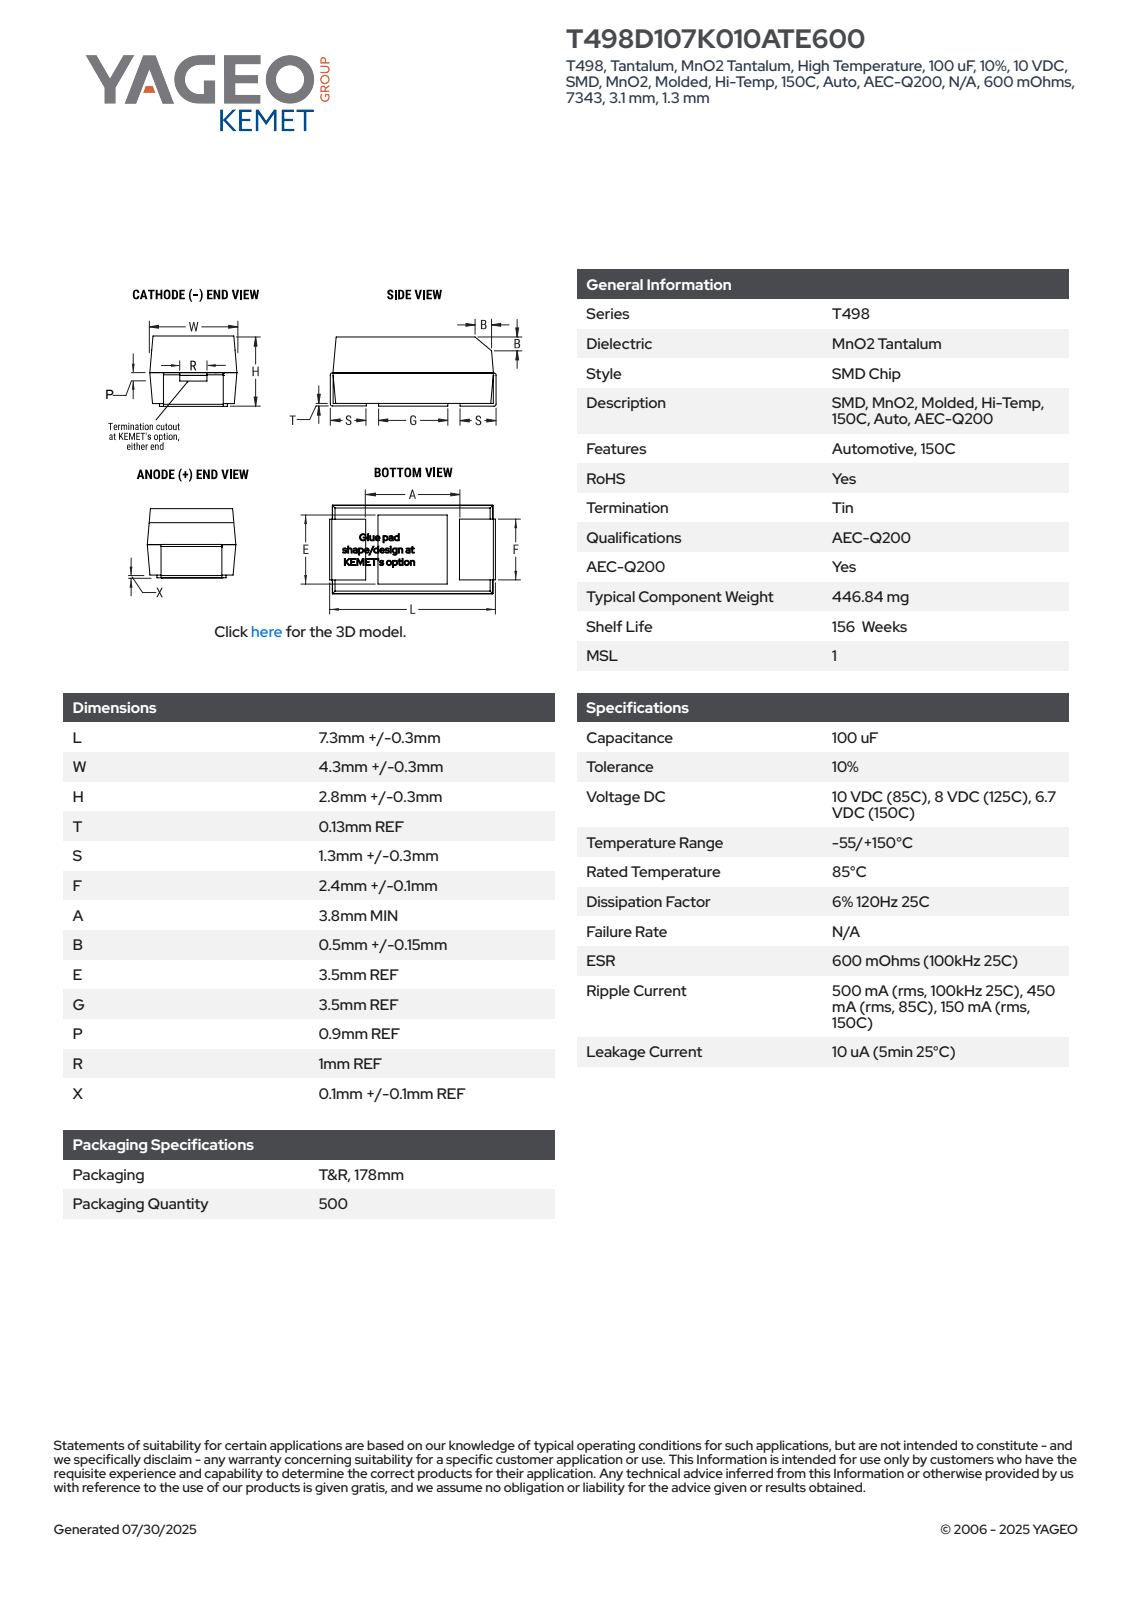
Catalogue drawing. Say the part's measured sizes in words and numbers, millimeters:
The part is named "CTSM_TCM2NK_7343_L7.6W4.6H3.1T0.13S1.3F2.5A3.8B0.65E3.5G3.5P0.9R1X0.2". Its 3-D file was written by "SolidWorks 2020 (AUTOMOTIVE_DESIGN)". It is 4 solids with 100 faces: 95 planar, 5 cylindrical and 0 other. Overall it measures 7.6 by 4.6 by 3.1 millimeters. Its volume is 93 cubic millimeters and its surface area 153 square millimeters. Partial cylindrical surfaces (rounded edges, fillets, slot ends): 4 of radius 0.1. The main face-to-face distances are 3.1, 2.9, 4.53, 4.54, 2.97, 7.47, 7.6, 7.34, 2.05, 5.55.
